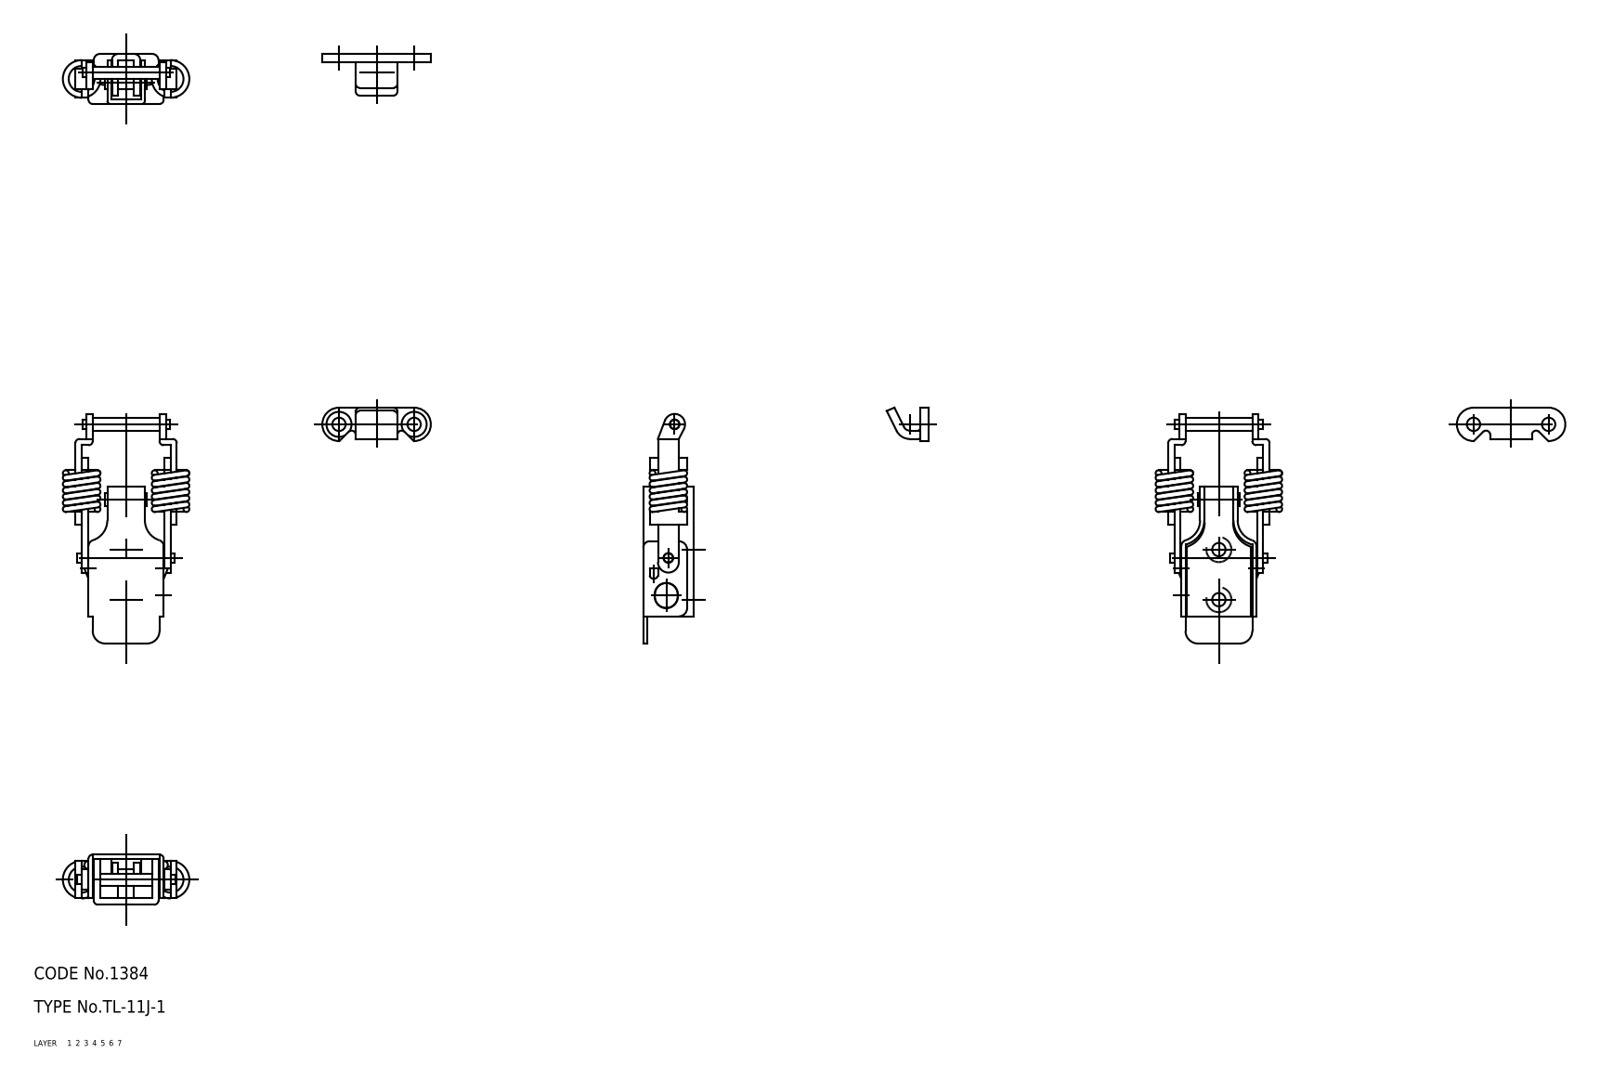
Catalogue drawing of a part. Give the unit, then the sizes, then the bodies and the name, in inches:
Units: inches
Overall size (bounding box): 2.224 × 1.193 × 0.472
Volume: 0.251 in³ · Surface area: 12.55 in²
Bodies: 12 solids, 430 faces (0 planar, 0 cylindrical, 430 other)
Part name (STEP PRODUCT): spring_mr; spring; shaft_C; shaft_B (+8 more)
STEP written by: CADfix (AUTOMOTIVE_DESIGN)
